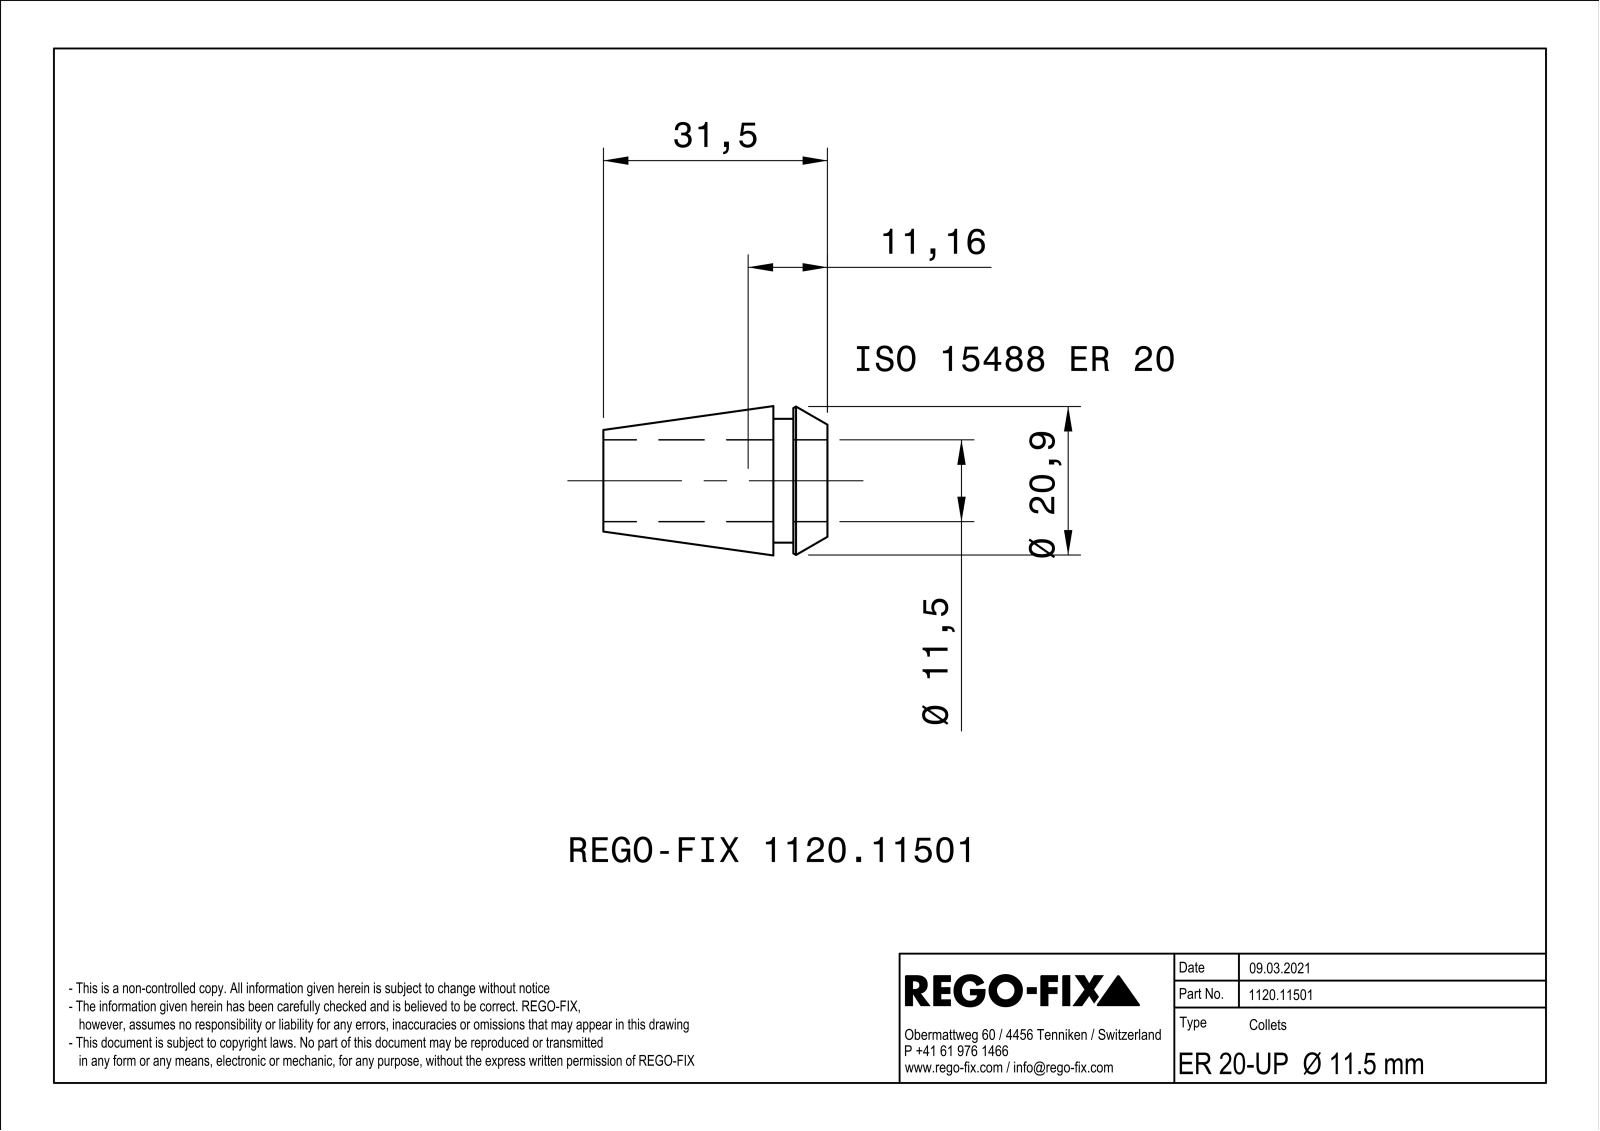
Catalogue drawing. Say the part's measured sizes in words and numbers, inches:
The part is named "NOCUT". Its 3-D file was written by "SIEMENS PLM Software Solid Edge ST10 (AUTOMOTIVE_DESIGN)". It is 1 solid with 177 faces: 88 planar, 9 cylindrical and 80 other. Overall it measures 1.24 by 0.826 by 0.826 inches. Its volume is 0.23 cubic inches and its surface area 8.545 square inches. Round holes: 1 of diameter 0.453. Round bosses or shafts: 1 of diameter 0.685. The main face-to-face distances are 0.024, 0.11, 0.189, 0.299, 1.24, 1.051, 0.941, 0.217, 0.028, 0.083.
